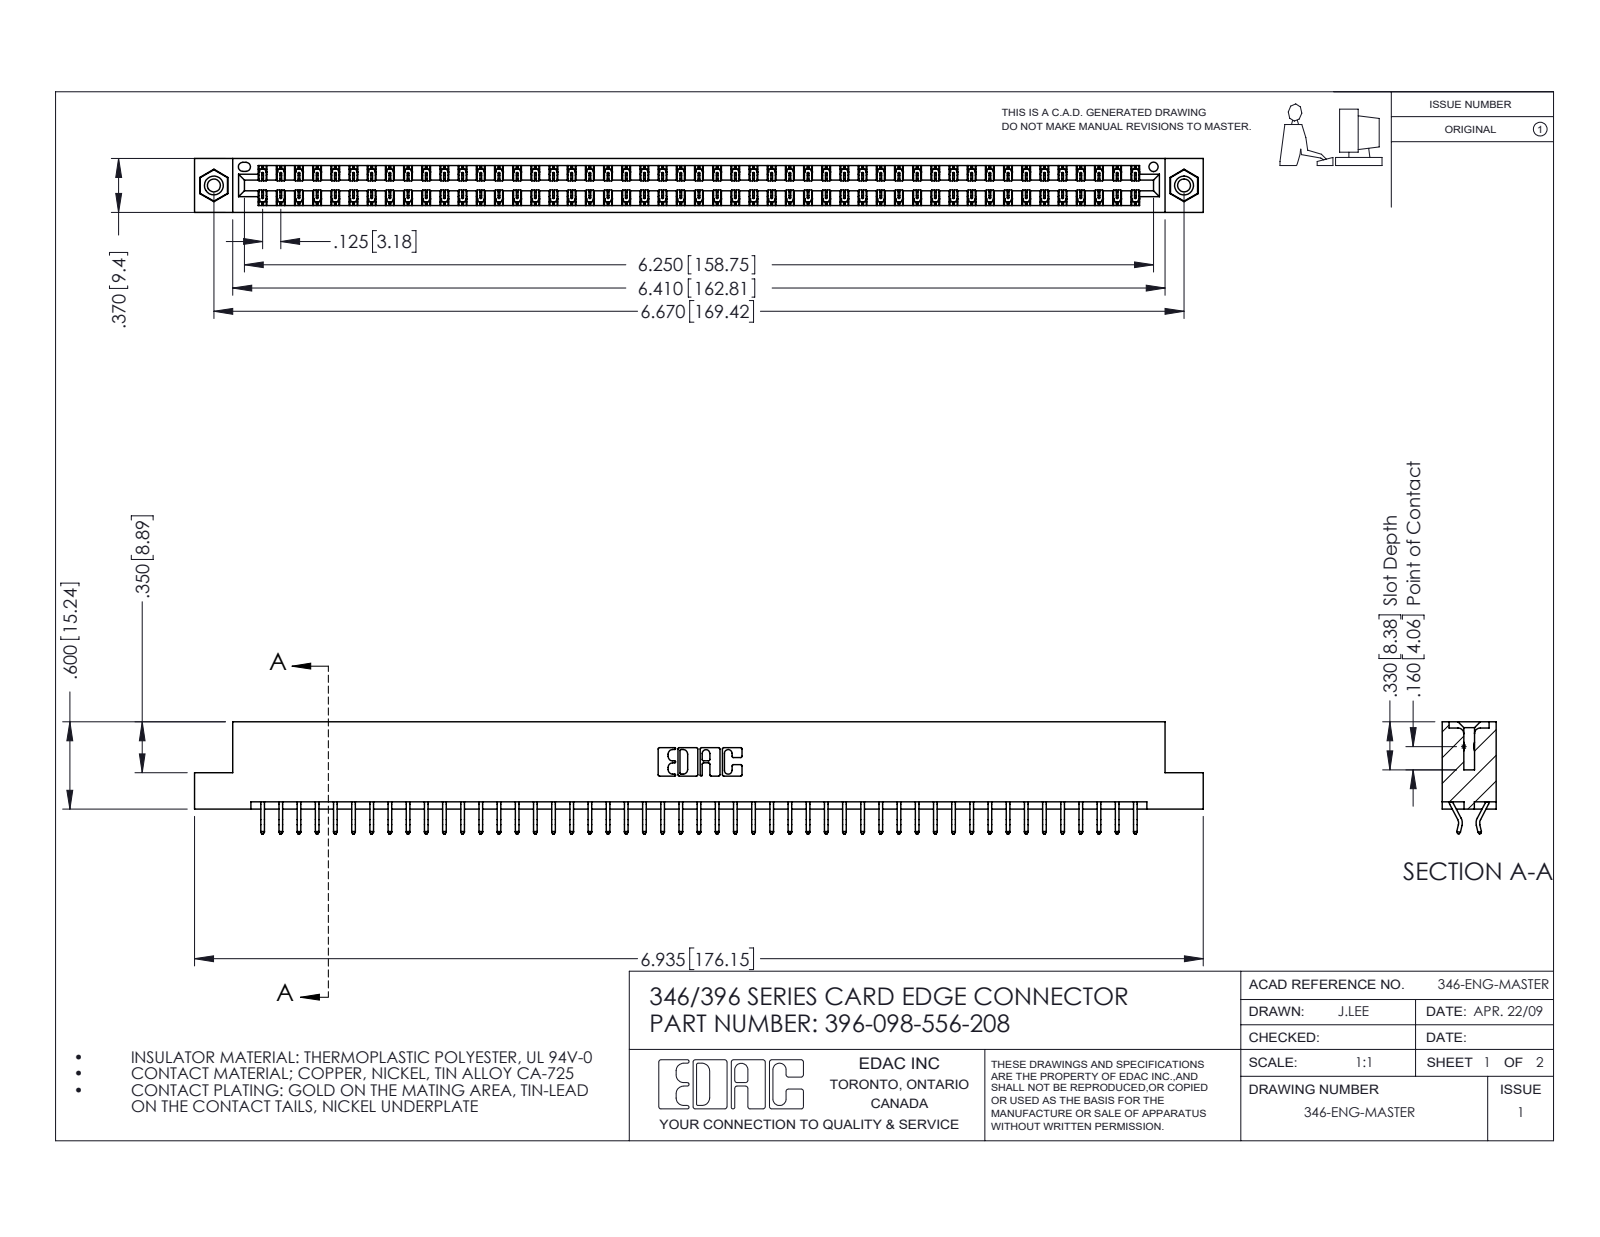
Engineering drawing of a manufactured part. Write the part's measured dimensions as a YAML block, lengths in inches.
part_name: "345-292-001_556 Tail; 345-250-001_345-250-003-102; 346 Part_Flush Mounting Lugs - 0.156 Dia-TI; 396-098-556-208"
step_written_by: "SolidWorks 2016 (CONFIG_CONTROL_DESIGN)"
units: inches
bodies: {solids: 101, faces: 5866, planar: 3930, cylindrical: 1920, other: 16}
overall_size: [6.935, 0.77, 0.37]
volume: 1.051
surface_area: 36.75
round_holes:
  - {diameter: 0.089, count: 2}
  - {diameter: 0.125, count: 2}
  - {diameter: 0.156, count: 2}
  - {diameter: 0.064, count: 1}
round_bosses_or_shafts:
  - {diameter: 0.155, count: 2}
partial_cylinders:
  - {radius: 0.006, count: 147}
  - {radius: 0.01, count: 22}
  - {radius: 0.007, count: 6}
  - {radius: 0.031, count: 6}
  - {radius: 0.026, count: 3}
  - {radius: 0.01, count: 2}
  - {radius: 0.014, count: 2}
  - {radius: 0.022, count: 2}
face_to_face_distances: [0.048, 0.322, 0.37, 0.25, 0.025, 0.072, 0.298, 0.275, 0.148, 0.222]
hole_center_spacings: [0.246, 6.461, 6.67]
